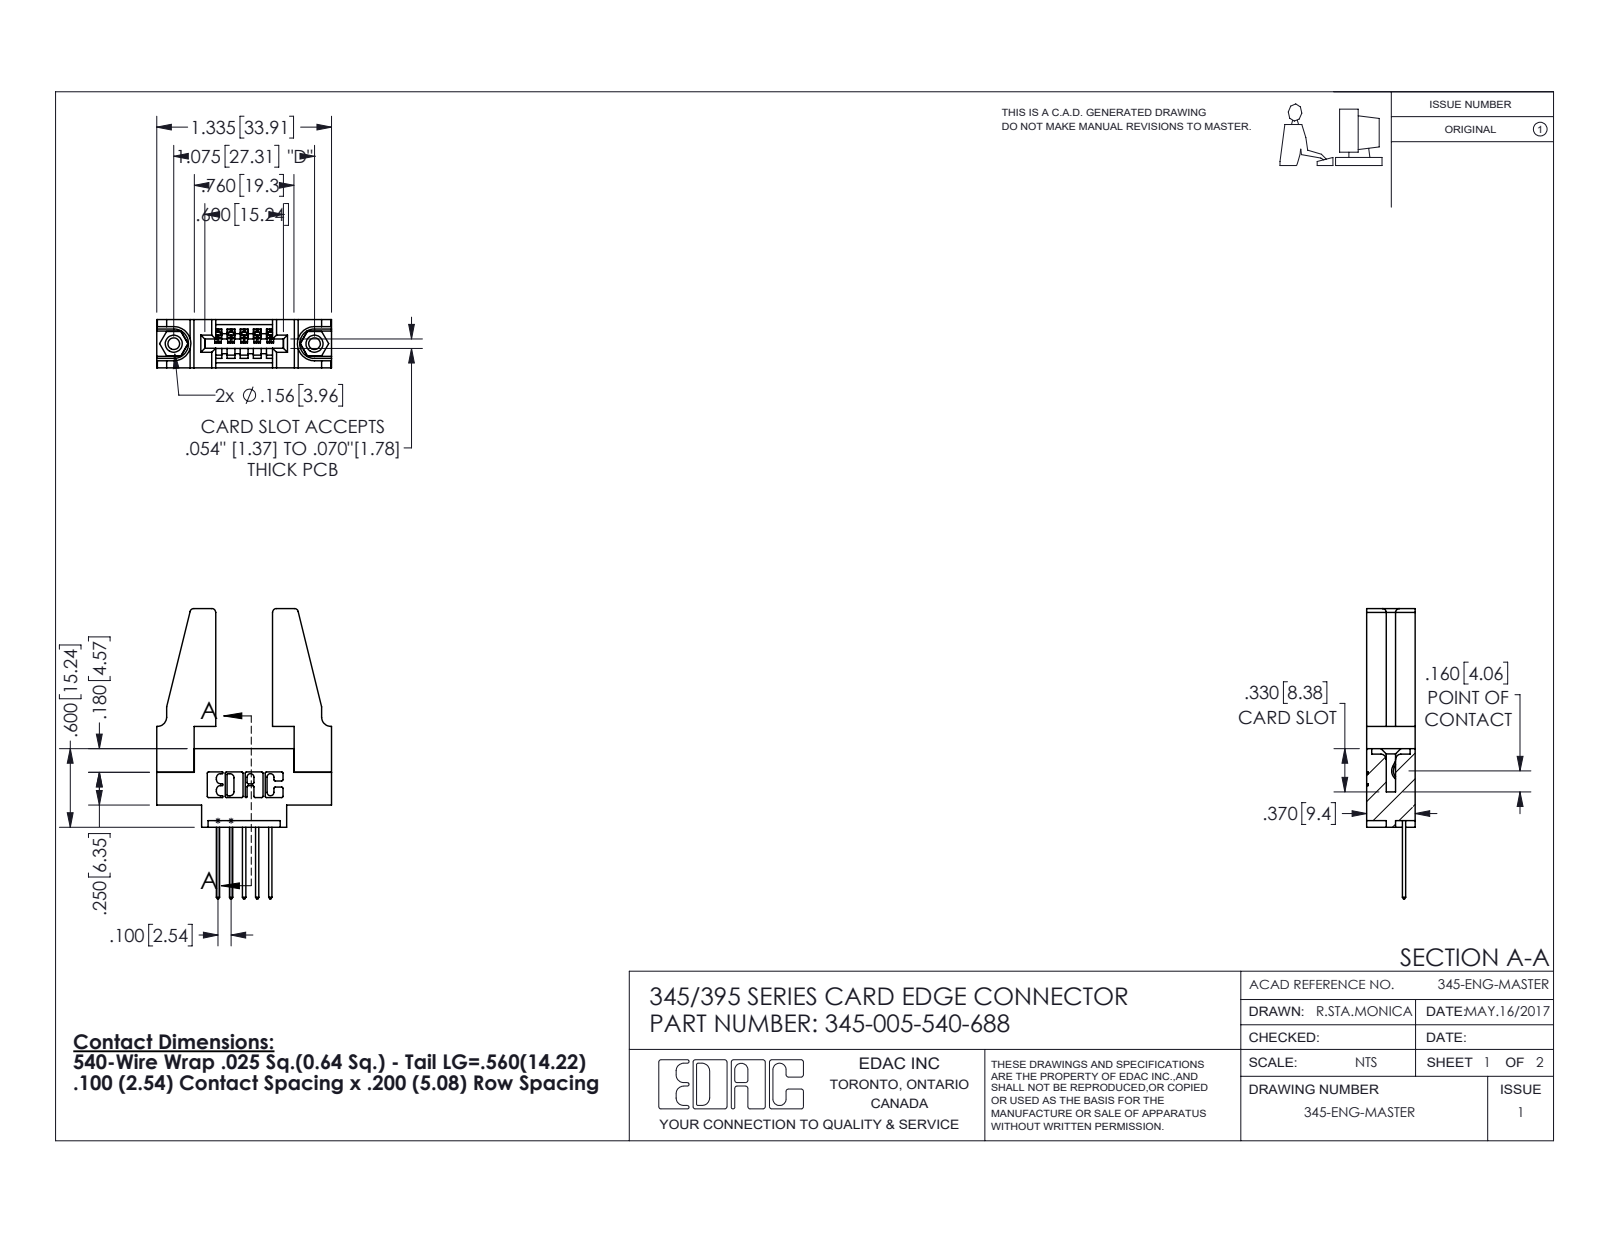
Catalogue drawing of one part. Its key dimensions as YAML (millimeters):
part_name: "345-250-001_345-250-001-102; 345 Part_0.170 Offset - 0.156 Dia-TH; 345-220-078_345-220-088; 345-292-001_345-293-140 (+1 more)"
step_written_by: "SolidWorks 2016 (CONFIG_CONTROL_DESIGN)"
units: millimeters
bodies: {solids: 10, faces: 544, planar: 356, cylindrical: 172, other: 16}
overall_size: [56.3, 33.9, 9.4]
volume: 6060
surface_area: 6542
round_holes:
  - {diameter: 2.3, count: 2}
  - {diameter: 3.2, count: 2}
  - {diameter: 4, count: 2}
  - {diameter: 1.6, count: 1}
round_bosses_or_shafts:
  - {diameter: 3.9, count: 2}
partial_cylinders:
  - {radius: 0.3, count: 22}
  - {radius: 0.2, count: 10}
  - {radius: 0.3, count: 10}
  - {radius: 0.8, count: 8}
  - {radius: 0.2, count: 6}
  - {radius: 0.8, count: 6}
  - {radius: 0.7, count: 3}
  - {radius: 0.8, count: 2}
face_to_face_distances: [9.4, 1.8, 7.6, 5.1, 3.8, 3.8, 5.6, 2, 2.5, 6.9]
hole_center_spacings: [6.9, 21.5, 27.3]
